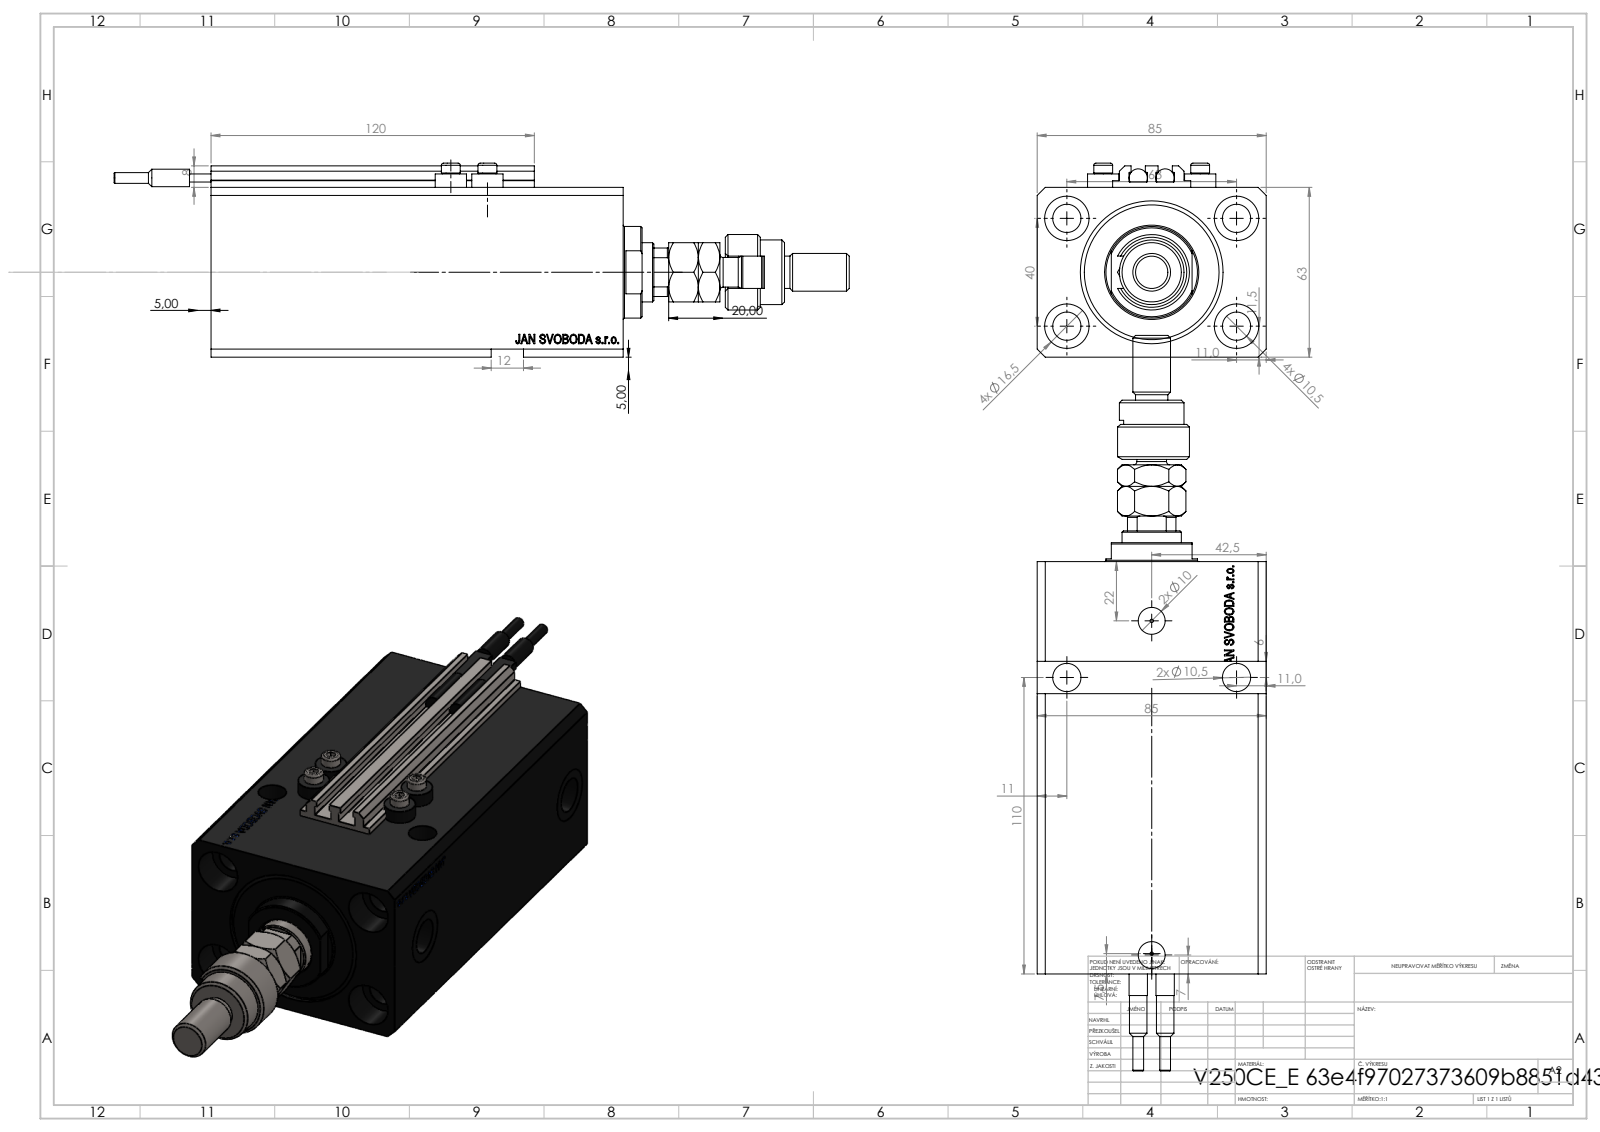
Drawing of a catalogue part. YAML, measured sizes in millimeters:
part_name: "V250CE_VC_E; V250CE_E_Body; MFA; V250CE_C_VCP (+3 more)"
step_written_by: "SolidWorks 2019 (CONFIG_CONTROL_DESIGN)"
units: millimeters
bodies: {solids: 12, faces: 1244, planar: 595, cylindrical: 171, other: 478}
overall_size: [273, 85, 72]
volume: 709336
surface_area: 151534
round_holes:
  - {diameter: 10.5, count: 8}
  - {diameter: 1.25, count: 4}
  - {diameter: 4, count: 4}
  - {diameter: 16.5, count: 4}
  - {diameter: 10, count: 2}
  - {diameter: 13.16, count: 2}
  - {diameter: 20, count: 2}
  - {diameter: 12.5, count: 1}
  - {diameter: 22, count: 1}
  - {diameter: 40, count: 1}
  - {diameter: 53, count: 1}
round_bosses_or_shafts:
  - {diameter: 11.6, count: 4}
  - {diameter: 7, count: 4}
  - {diameter: 6.8, count: 2}
  - {diameter: 6.5, count: 2}
  - {diameter: 4, count: 2}
  - {diameter: 34, count: 1}
  - {diameter: 28, count: 1}
  - {diameter: 24, count: 1}
partial_cylinders:
  - {radius: 0.2, count: 10}
  - {radius: 9.75, count: 1}
  - {radius: 10.5, count: 1}
face_to_face_distances: [63, 85, 17, 153, 136, 3, 65, 11.4, 124.6, 141.6]
hole_center_spacings: [37.31, 63, 13.6, 15.4, 24.96, 33.62, 36, 37.86]
